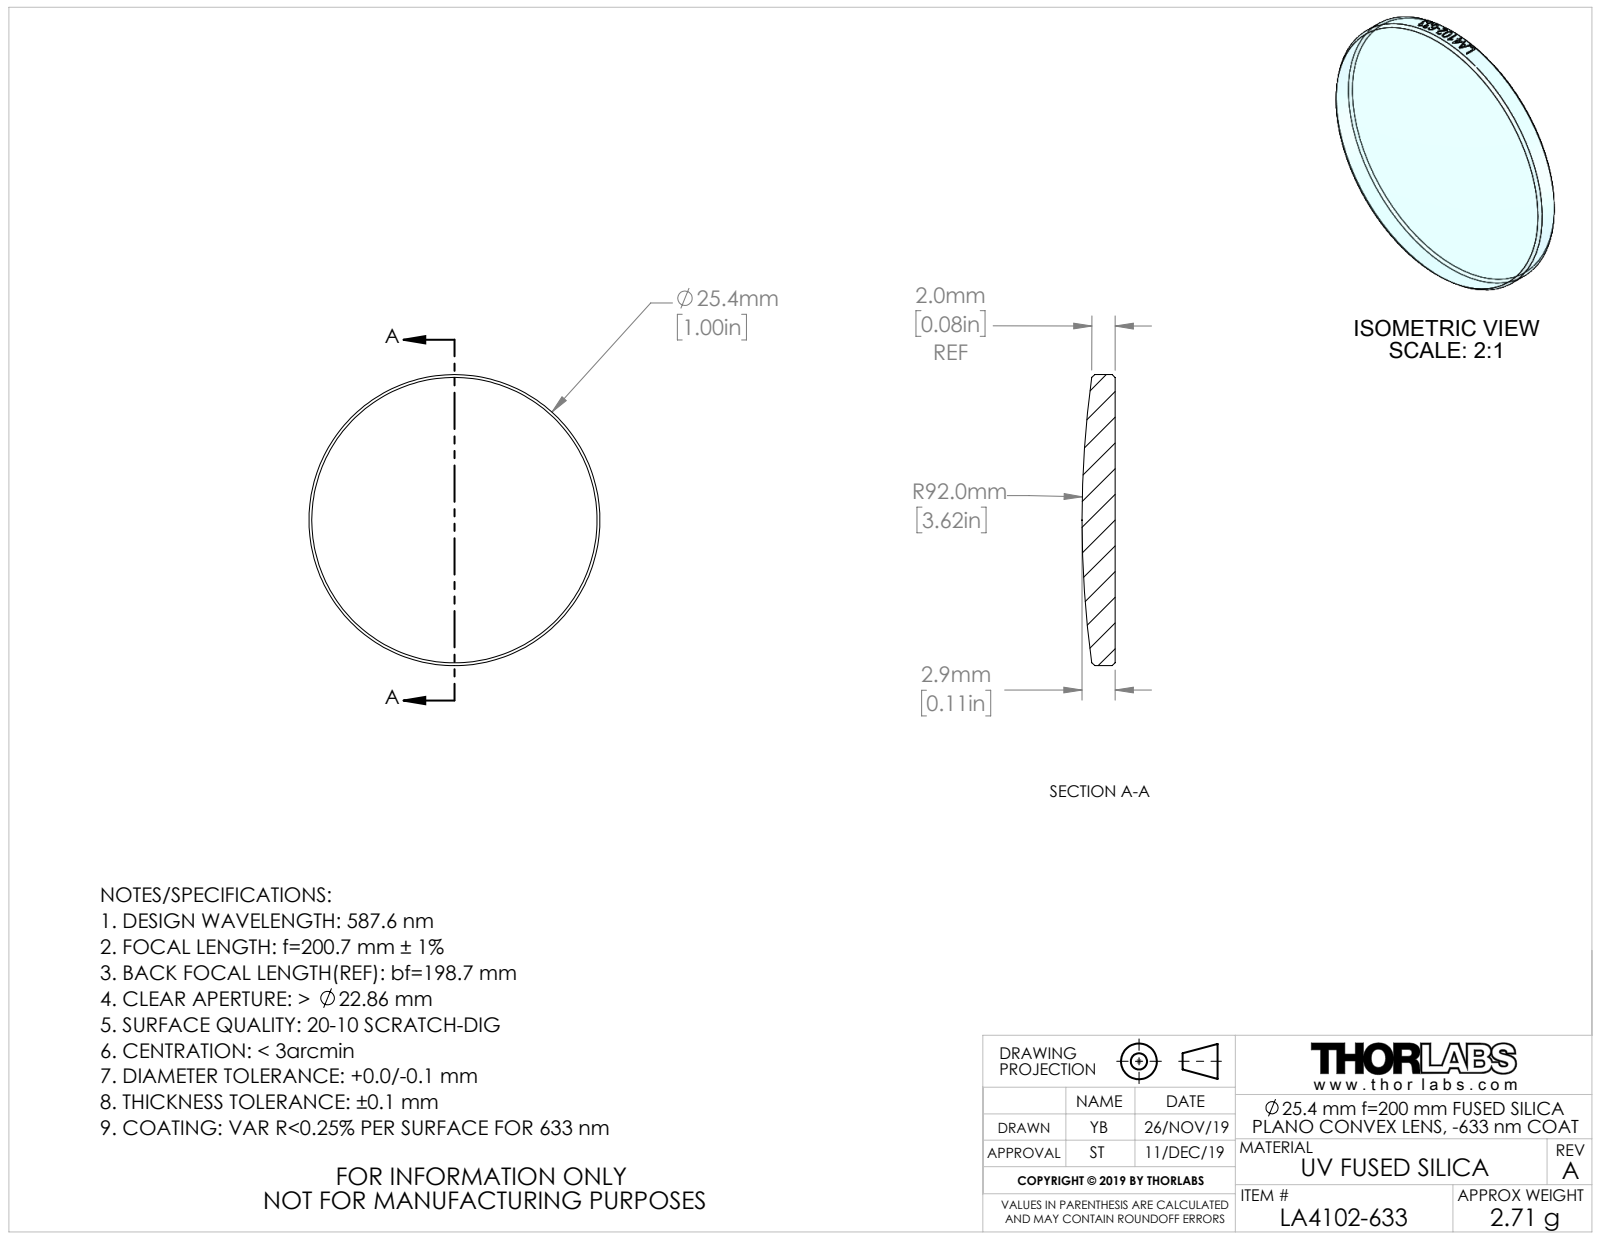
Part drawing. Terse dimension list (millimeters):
name: CTN015000-999; CTN015019
written by: SolidWorks 2018 (AUTOMOTIVE_DESIGN)
unit: mm
bodies: 1 solid, 25 faces (1 planar, 18 cylindrical, 6 other)
size: 25.4 × 25.4 × 2.88
volume: 1 232 mm³; area: 1 154 mm²
bosses: 1× ⌀25.4
